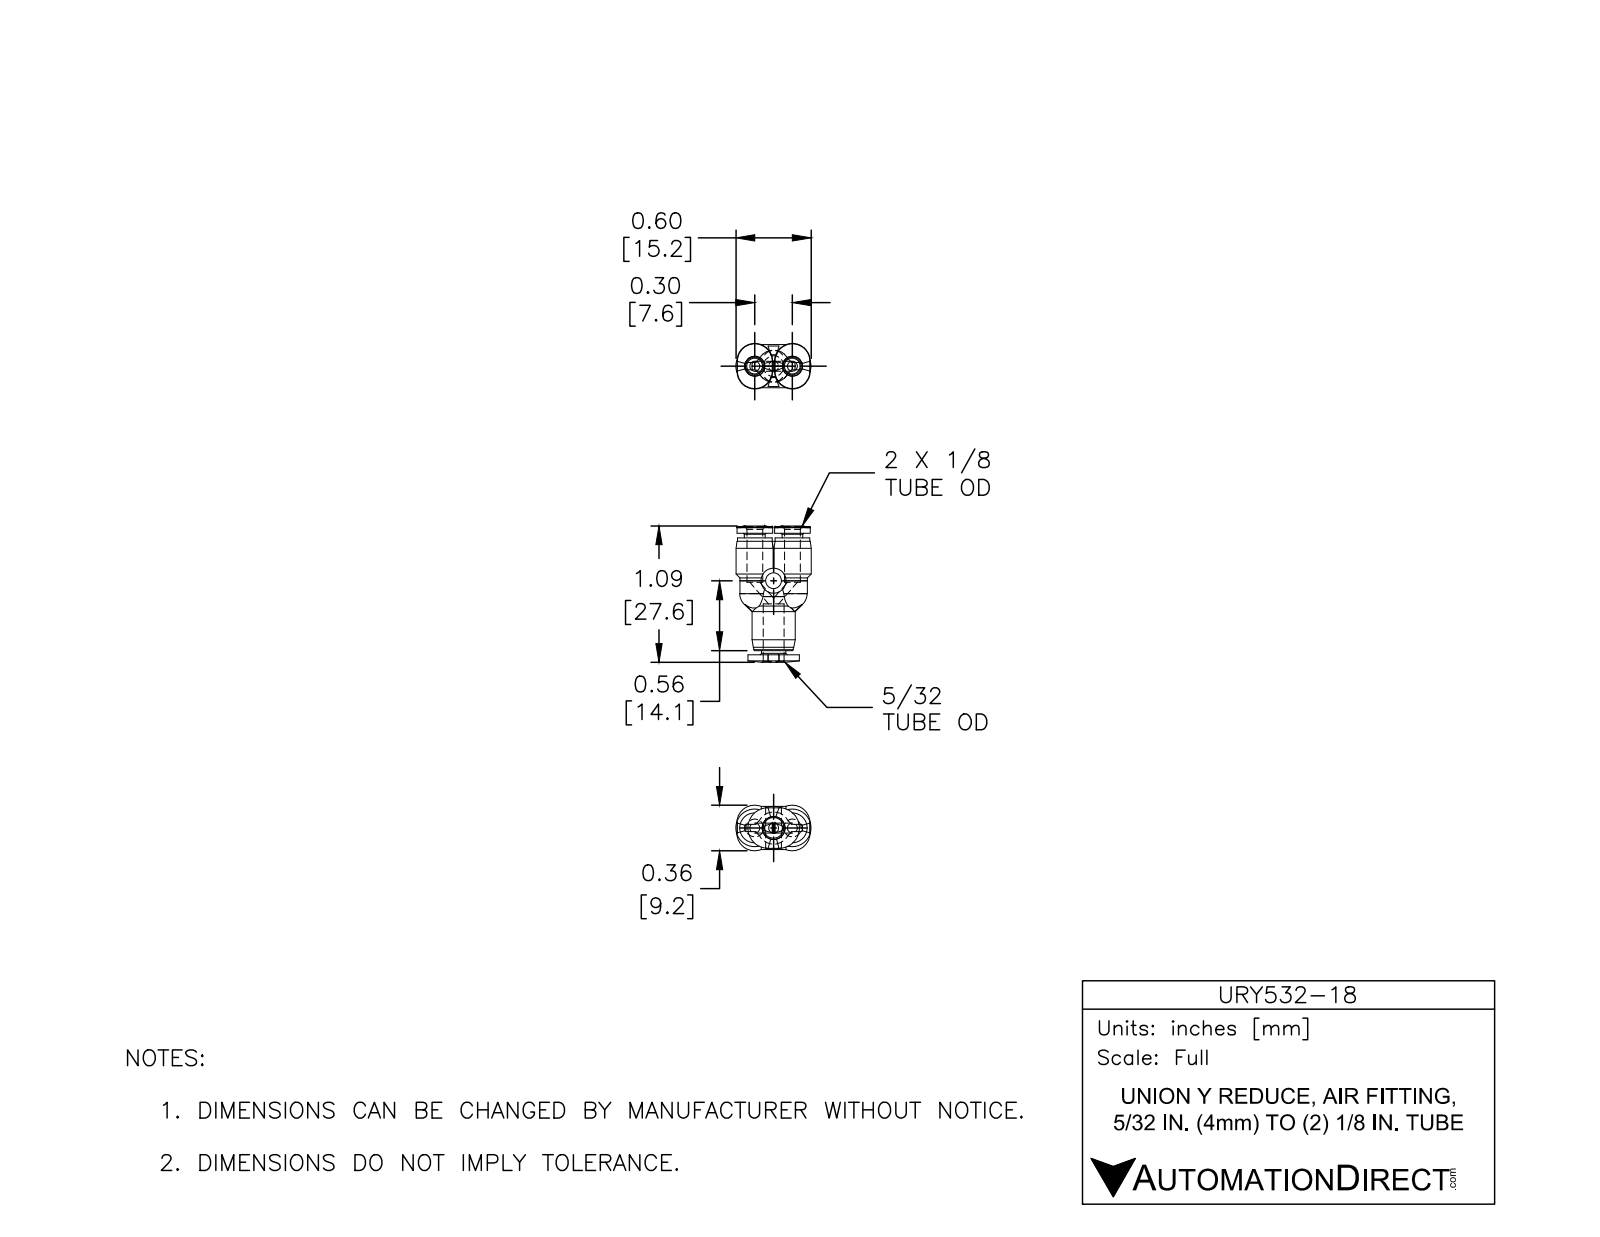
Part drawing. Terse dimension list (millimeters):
name: URY532-18
written by: SolidWorks 2015 (CONFIG_CONTROL_DESIGN)
unit: mm
bodies: 1 solid, 136 faces (28 planar, 41 cylindrical, 67 other)
size: 27.6 × 15.2 × 9.2
volume: 1 500 mm³; area: 1 906 mm²
holes: 3× ⌀3.2, 1× ⌀4.2
bosses: 2× ⌀7.6, 2× ⌀7, 2× ⌀4.2, 1× ⌀8.7, 1× ⌀8, 1× ⌀5, 1× ⌀4.9
rounds: 4× R3.6, 2× R3, 2× R4.1, 1× R3.3
face distances: 0.9, 23.6, 24.6, 0.8, 22.8, 23.7, 8.7, 10.3, 9.4, 13.4
hole spacings: 3.8, 7.6
